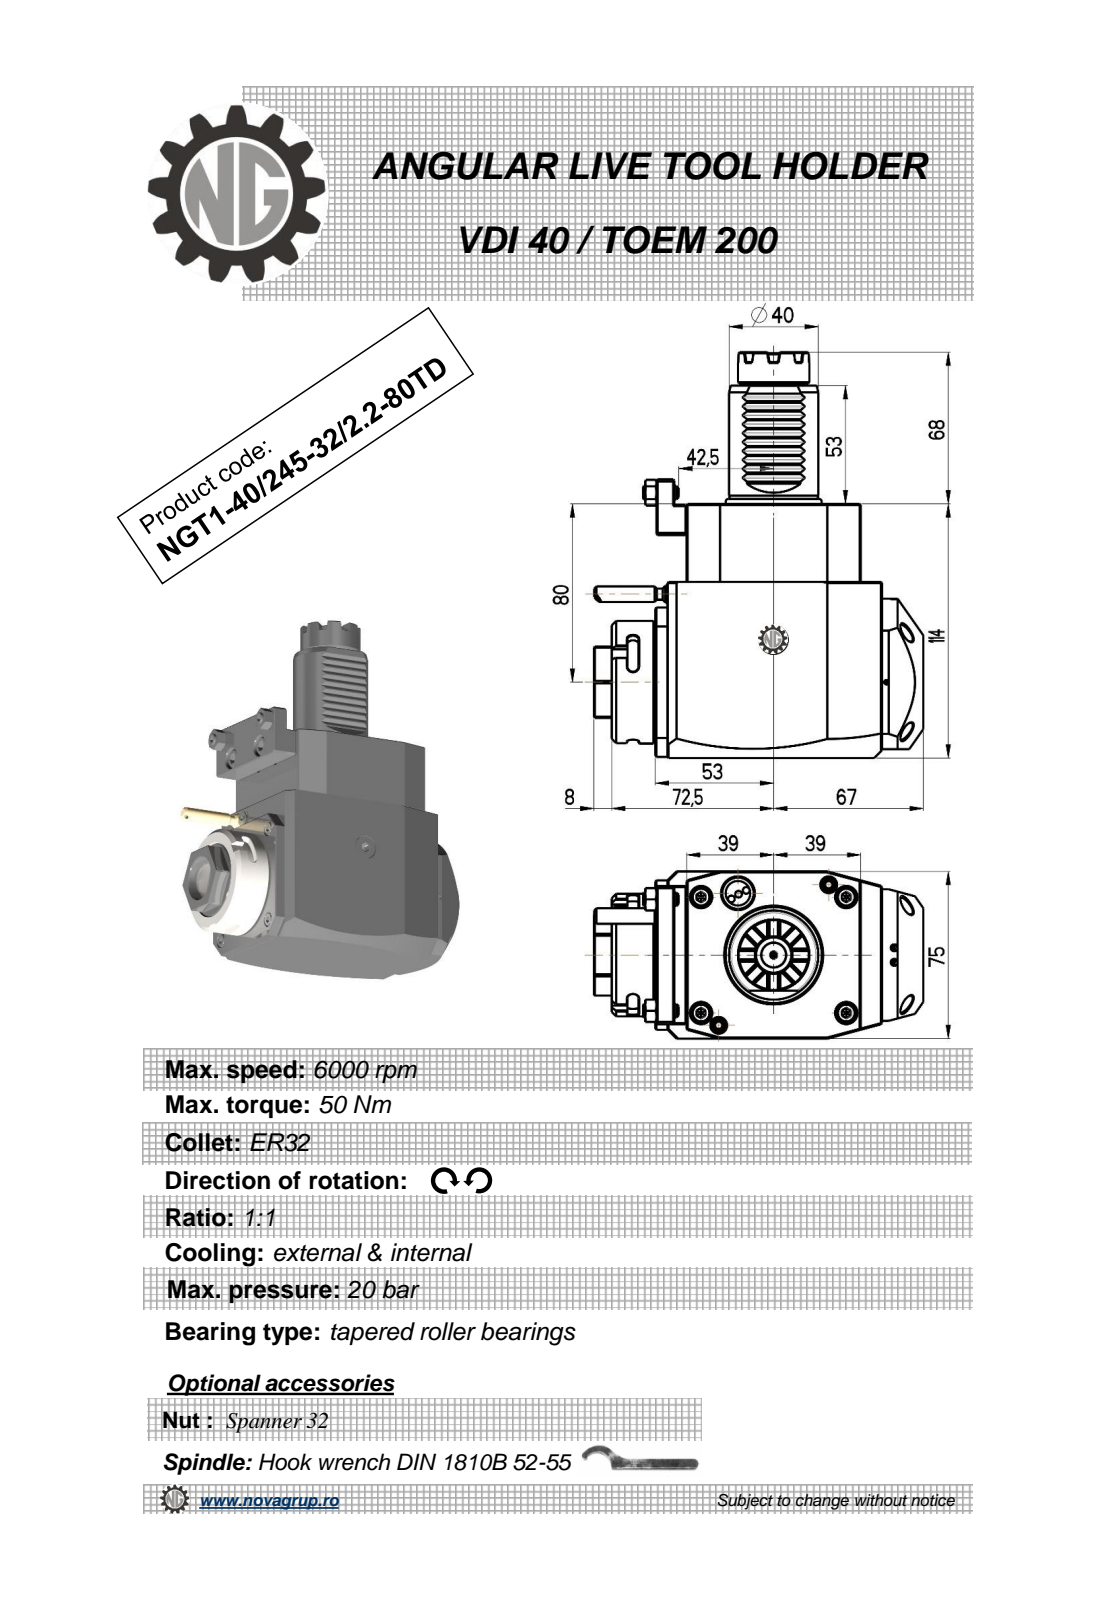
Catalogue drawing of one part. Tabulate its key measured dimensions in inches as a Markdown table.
| quantity | value |
| --- | --- |
| part name | NGT1_40_245_32_1_2_80TD |
| STEP written by | PRO/ENGINEER BY PARAMETRIC TECHNOLOGY CORPORATION, 2010280 (CONFIG_CONTROL_DESIGN) |
| units | inches |
| bodies | 1 solid, 421 faces (225 planar, 66 cylindrical, 130 other) |
| overall size | 7.165 × 5.807 × 2.953 |
| volume | 59.19 in³ |
| surface area | 113.8 in² |
| round holes (diameter × count) | 0.098 × 1, 0.118 × 1, 0.906 × 1 |
| round bosses / shafts (diameter × count) | 0.236 × 2, 2.165 × 1, 1.89 × 1, 1.575 × 1, 1.26 × 1, 0.677 × 1, 0.315 × 1, 0.276 × 1 |
| partial cylindrical surfaces (radius × count) | 0.012 × 10, 0.012 × 10, 0.098 × 6, 7.087 × 2, 0.02 × 1, 0.965 × 1, 1.476 × 1 |
| main face-to-face distances | 2.953, 4.488, 0.02, 0.551, 1.102, 3.622, 4.39, 0.531, 4.705, 0.768 |
| hole center spacings | 1.701 |
